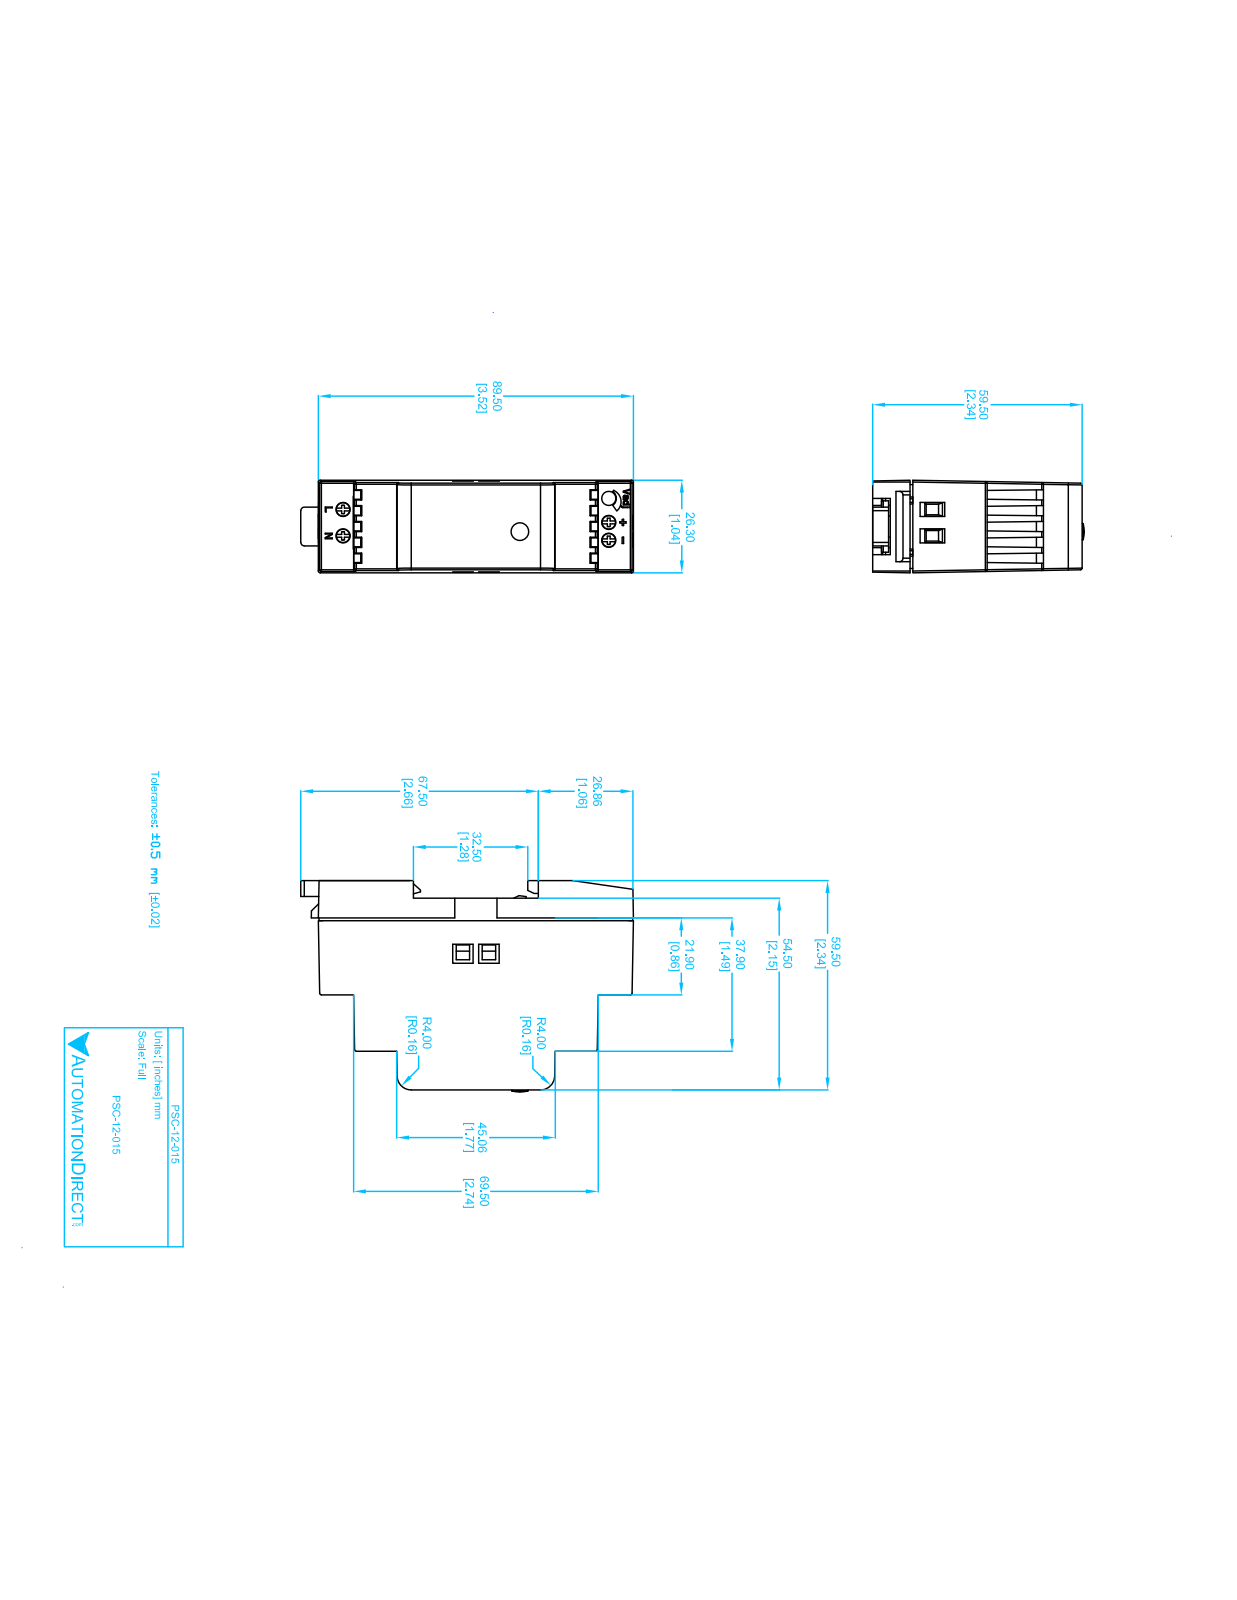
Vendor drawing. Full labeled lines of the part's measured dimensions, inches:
Part name (STEP PRODUCT): PSC-12-015 SLDPRT
STEP written by: SolidWorks 2011 (CONFIG_CONTROL_DESIGN)
Units: inches
Bodies: 1 solid, 441 faces (351 planar, 54 cylindrical, 36 other)
Overall size (bounding box): 3.719 × 2.372 × 1.039
Volume: 6.452 in³ · Surface area: 32.1 in²
Round holes (diameter × count): ⌀0.16 ×5
Round bosses / shafts (diameter × count): ⌀0.2 ×1
Partial cylindrical surfaces — rounded edges, fillets, slot ends (radius × count): R0.02 ×26, R0.04 ×2, R0.16 ×2
Main face-to-face distances: 1.039, 0.19, 0.595, 2.341, 2.151, 1.9, 0.44, 1.71, 0.441, 1.27
Hole centre spacings: 0.2, 0.25, 0.3, 0.45, 3.02, 3.021, 3.025, 3.028
